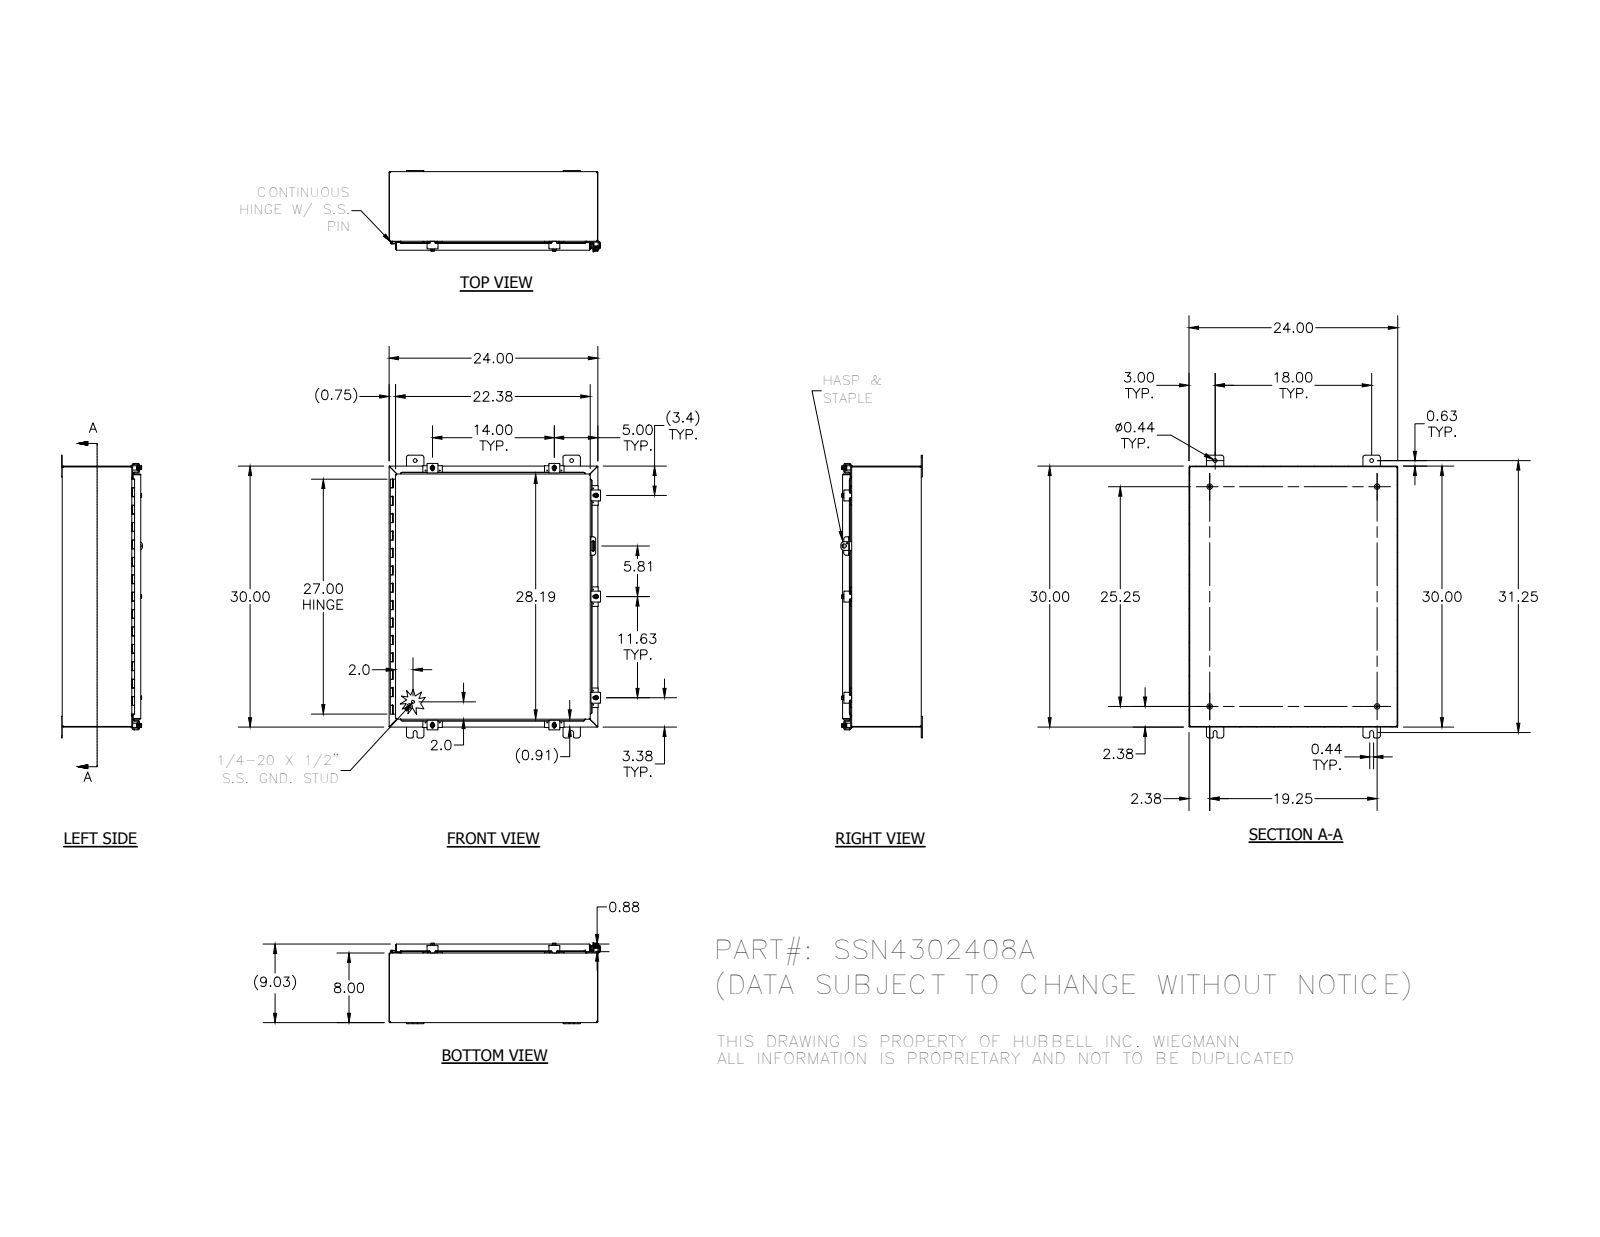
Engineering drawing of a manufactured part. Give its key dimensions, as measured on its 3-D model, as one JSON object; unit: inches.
{"part_name": "SSN43024ALID; 38412; 32874-30P; SSN4302408ABKP (+8 more)", "step_written_by": "SolidWorks 2014 (AUTOMOTIVE_DESIGN)", "units": "inches", "bodies": {"solids": 52, "faces": 2090, "planar": 818, "cylindrical": 905, "other": 367}, "overall_size": [32.5, 24.216, 9.355], "volume_in3": 207.8, "surface_area_in2": 5463, "round_holes": [[0.11, 14], [0.211, 7], [0.281, 7], [0.3, 7], [0.438, 4], [0.125, 1], [0.156, 1], [0.5, 1]], "round_bosses_or_shafts": [[0.25, 9], [0.52, 7], [0.5, 7], [0.35, 7], [0.625, 4], [0.33, 4], [0.337, 1], [0.12, 1]], "partial_cylinders_radius": [[0.03, 83], [0.125, 37], [0.25, 33], [0.031, 23], [0.105, 23], [0.062, 18], [0.141, 14], [0.1, 10]], "face_to_face_distances": [0.074, 8.959, 8.885, 9.033, 23.926, 29.926, 7.926, 1.033, 24, 23.852], "hole_center_spacings": [0.876, 29.3, 14, 1.625, 11.625, 12.442, 13.191, 14.816]}
